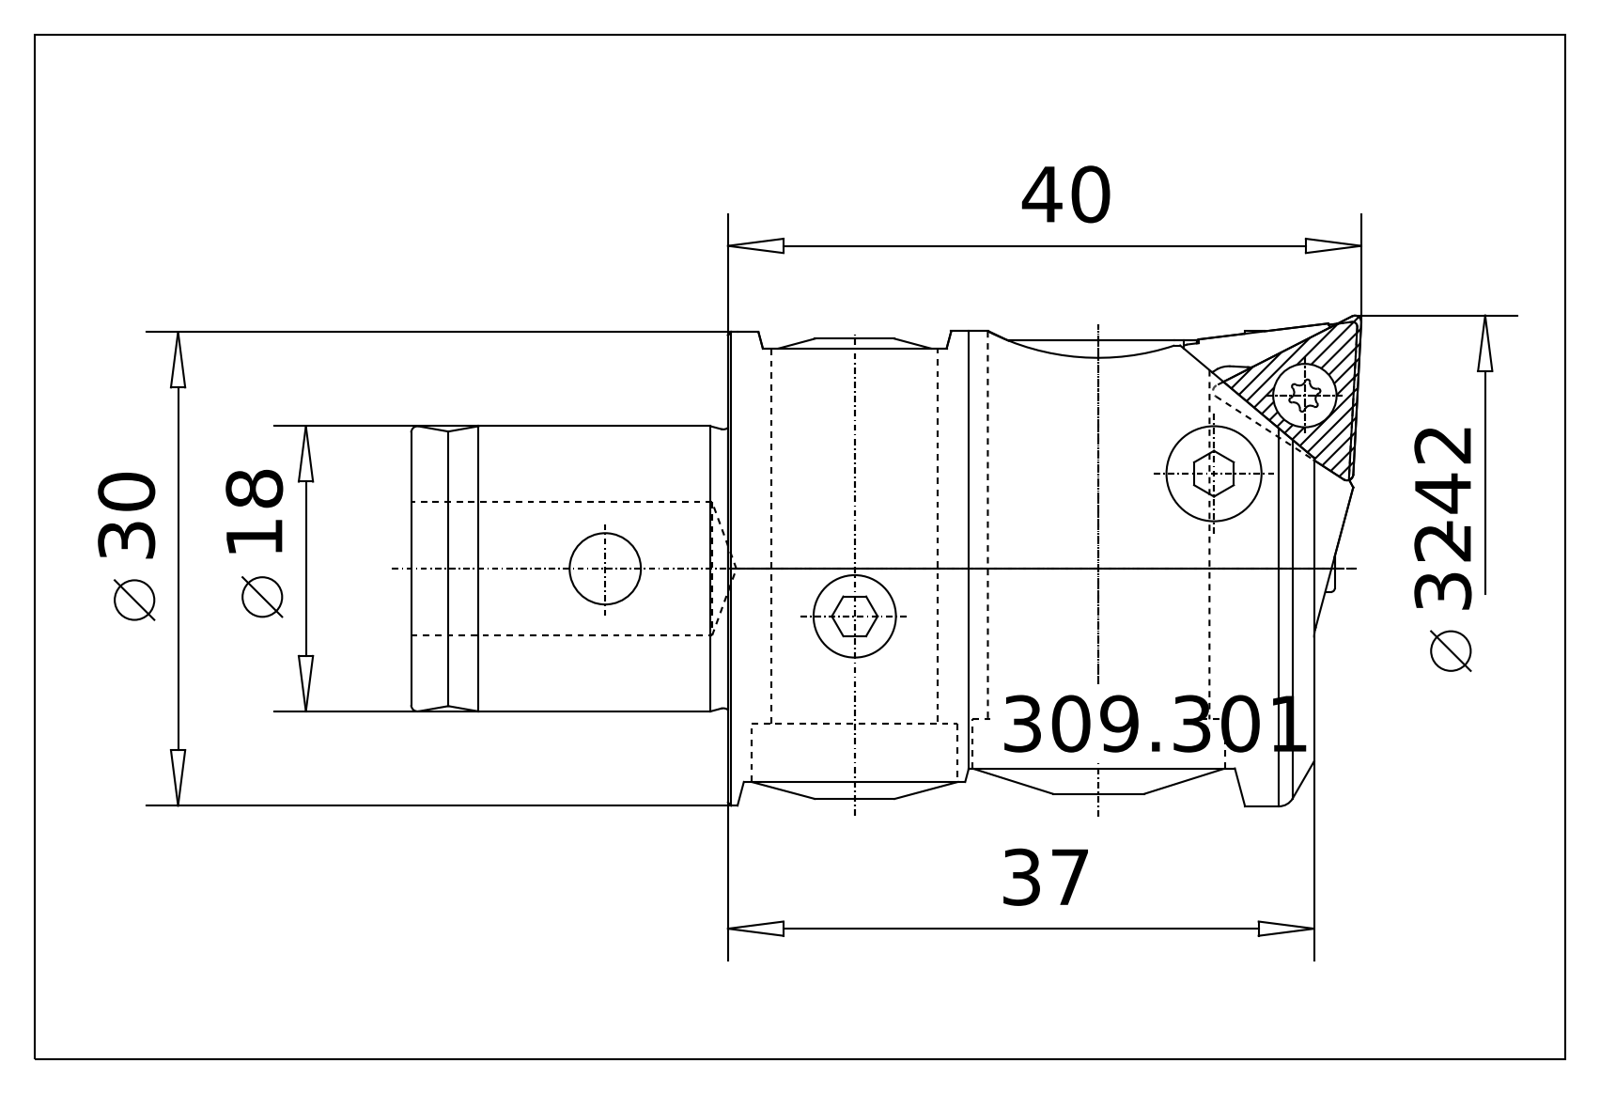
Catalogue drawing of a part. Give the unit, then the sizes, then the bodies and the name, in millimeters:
Units: millimetres
Overall size (bounding box): 59.98 × 31.07 × 30
Round holes (diameter × count): ⌀2.5 ×3, ⌀2 ×2, ⌀2.75 ×1, ⌀2.8 ×1, ⌀3.5 ×1, ⌀4.5 ×1, ⌀9 ×1, ⌀13 ×1, ⌀16 ×1
Round bosses / shafts (diameter × count): ⌀30 ×1, ⌀18 ×1, ⌀15.9 ×1, ⌀12.9 ×1, ⌀5.7 ×1, ⌀3.45 ×1, ⌀3 ×1, ⌀2.5 ×1
Partial cylindrical surfaces — rounded edges, fillets, slot ends (radius × count): R0.15 ×6, R0.4 ×6, R2 ×4, R1.6 ×3, R2.5 ×2, R3.05 ×2, R15 ×1
Main face-to-face distances: 28.7, 10, 8.3, 37, 57, 48.7, 20, 3.4, 6.6, 26.5
Hole centre spacings: 1.5, 9.65, 9.75, 15.4, 45.5, 45.66
Volume: 28 547 mm³ · Surface area: 9 049 mm²
Bodies: 5 solids, 378 faces (168 planar, 80 cylindrical, 130 other)
Part name (STEP PRODUCT): 309.301 Kaiser EWB 32 UP x CK3|690.179 Kaiser ETL M3x7.9;Schnitt-Rotation2; 309.301 Kaiser EWB 32 UP x CK3|627.131 Kaiser WPH EWB 32 UP|694.122 Kaiser ETL M2.5x6.5 T7 IP 10S_309.301;Kreismuster1; 309.301 Kaiser EWB 32 UP x CK3|627.131 Kaiser WPH EWB 32 UP|655.383 Kaiser TCGT 110204 K10C;Kombinieren1; 309.301 Kaiser EWB 32 UP x CK3|627.131 Kaiser WPH EWB 32 UP|627.131 Kaiser WPH EWB 32 UP;Verrundung5
STEP written by: ACIS (automotive_design)
